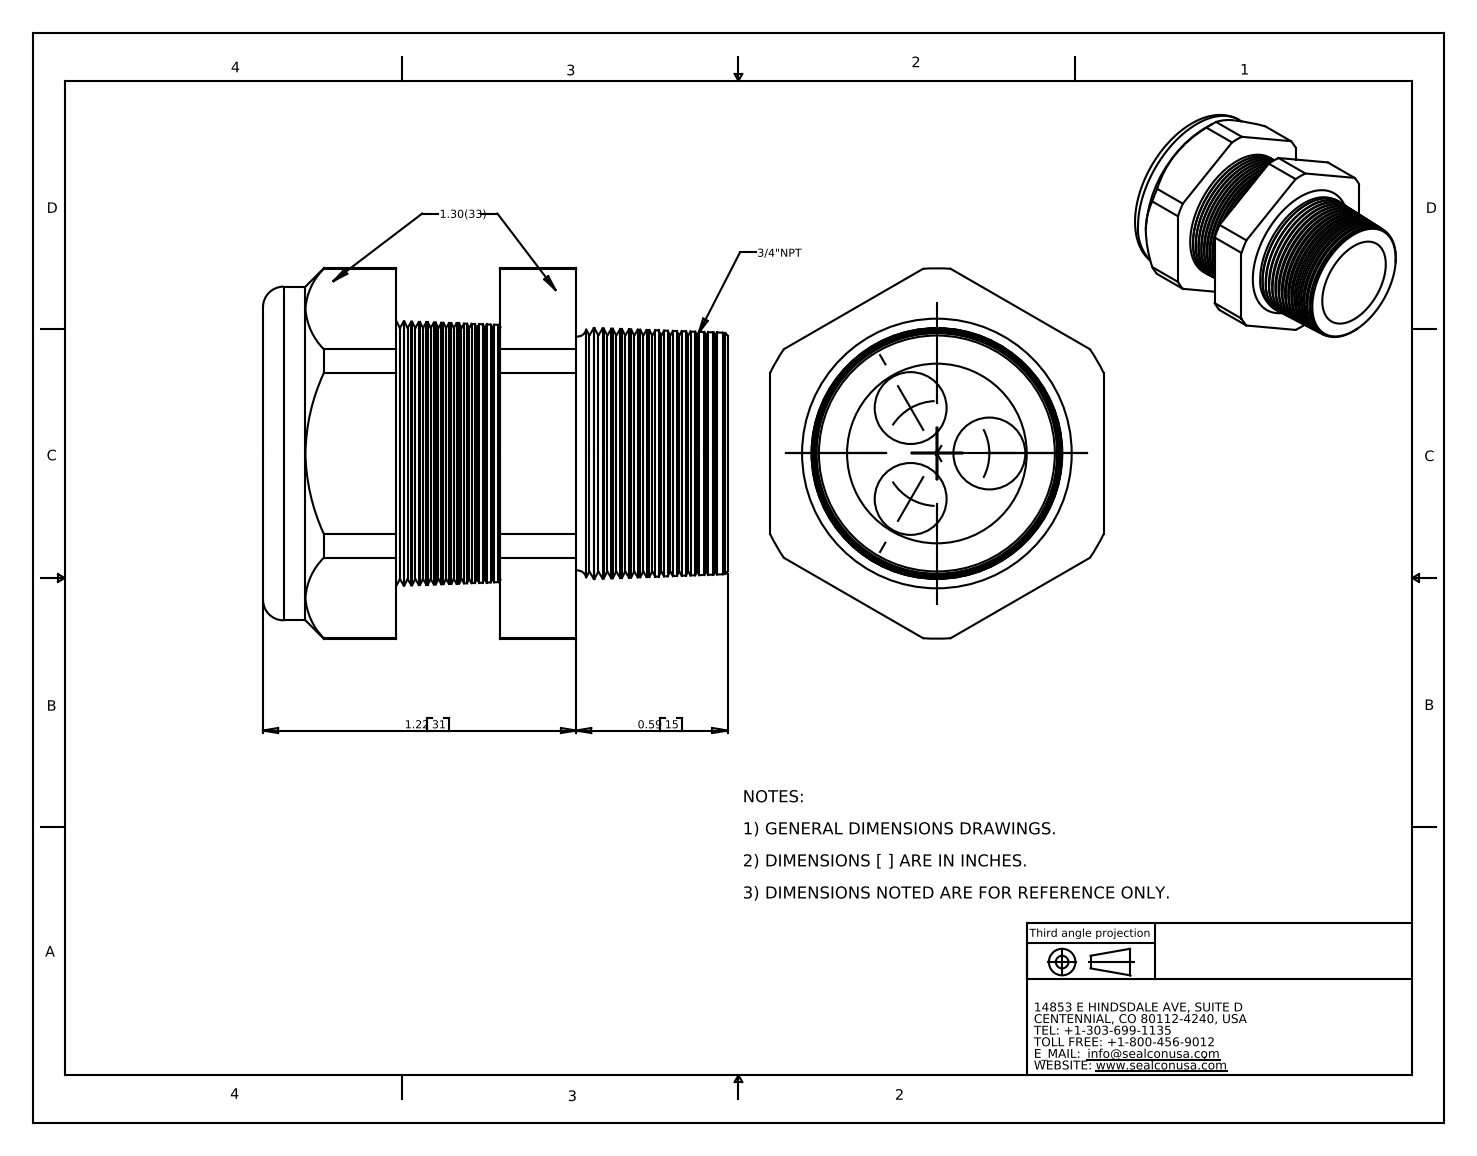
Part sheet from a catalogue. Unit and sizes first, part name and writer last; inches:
Units: inches
Overall size (bounding box): 1.81 × 1.443 × 1.3
Round holes (diameter × count): ⌀0.28 ×3, ⌀0.69 ×1, ⌀0.71 ×1
Round bosses / shafts (diameter × count): ⌀1.3 ×1
Partial cylindrical surfaces — rounded edges, fillets, slot ends (radius × count): R0.721 ×1
Main face-to-face distances: 1.3, 0.925, 0.52, 0.405, 1.22, 0.7, 0.295, 1.81, 1.29, 0.885
Hole centre spacings: 0.354, 0.205, 0.204
Volume: 1.243 in³ · Surface area: 18.09 in²
Bodies: 2 solids, 240 faces (20 planar, 26 cylindrical, 194 other)
Part name (STEP PRODUCT): CD21N2-BK
STEP written by: SolidWorks 2007 (CONFIG_CONTROL_DESIGN)
